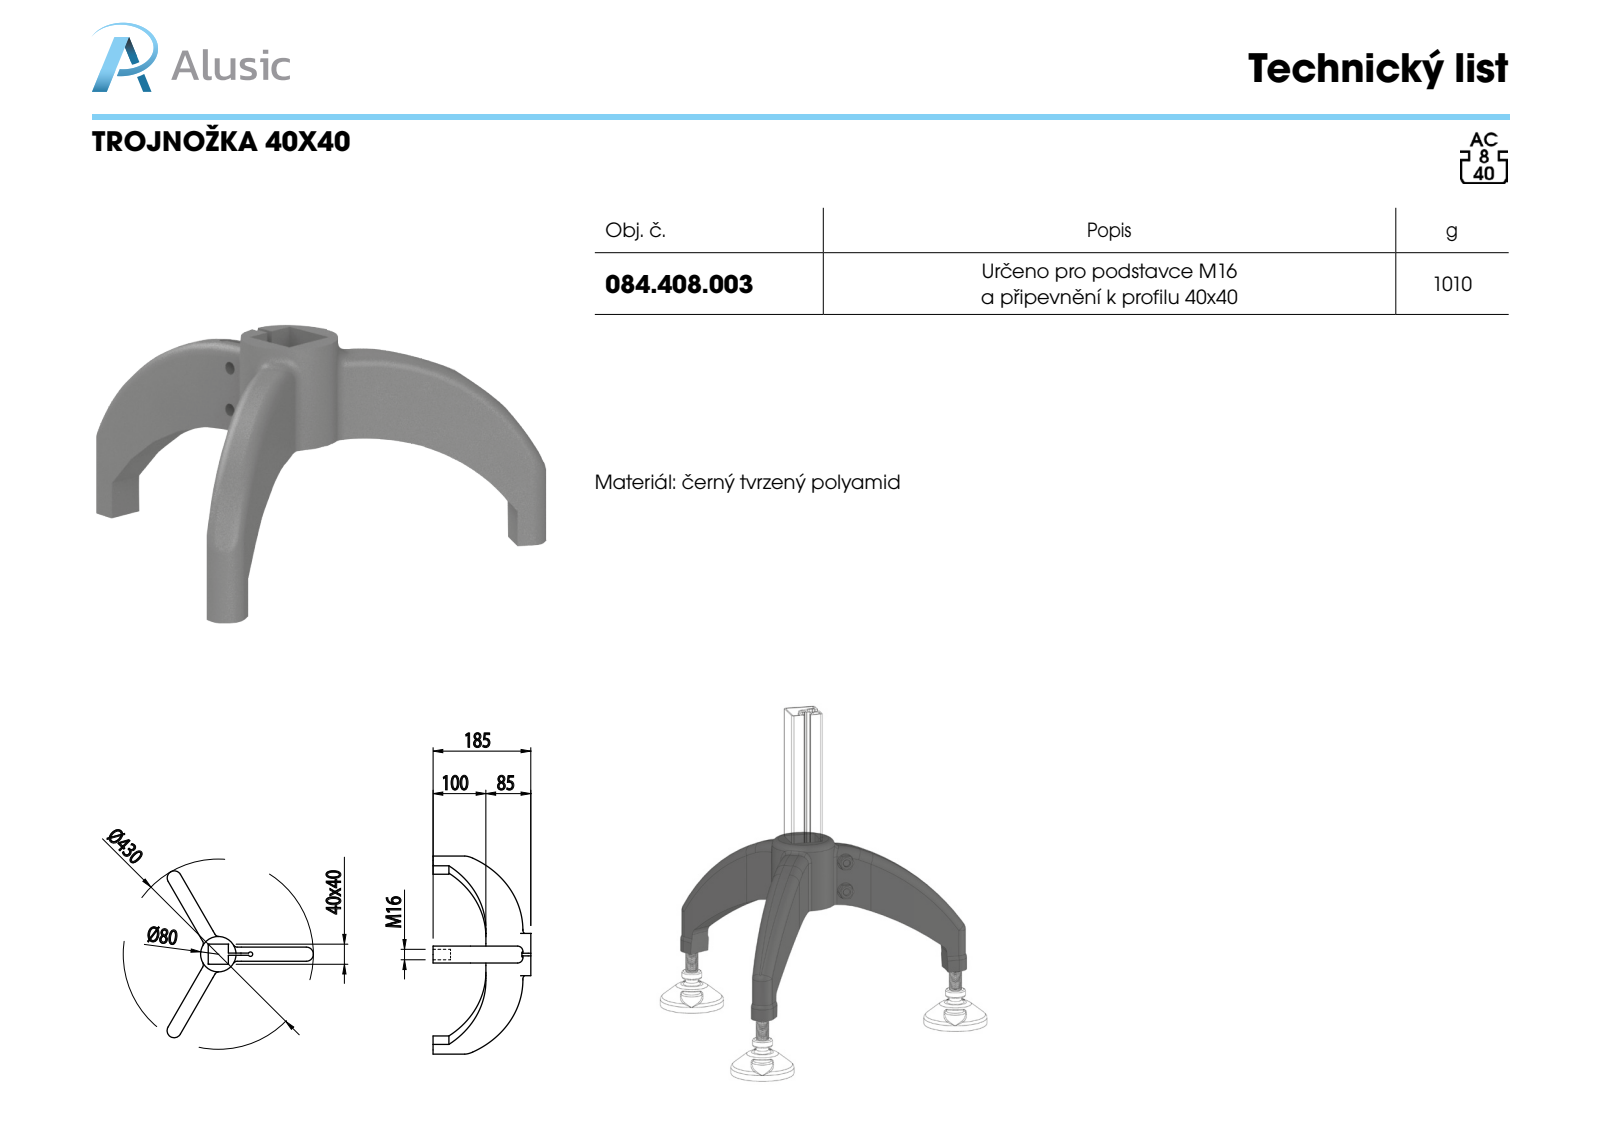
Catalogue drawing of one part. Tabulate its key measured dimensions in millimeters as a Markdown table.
| quantity | value |
| --- | --- |
| part name | 084.408.003 |
| STEP written by | SolidWorks 2016 (CONFIG_CONTROL_DESIGN) |
| units | millimeters |
| bodies | 0 solids, 222 faces (54 planar, 60 cylindrical, 108 other) |
| overall size | 375.39 × 328.98 × 185 |
| round holes (diameter × count) | 14 × 3, 10 × 2, 8 × 1 |
| round bosses / shafts (diameter × count) | 21 × 2, 19 × 2 |
| partial cylindrical surfaces (radius × count) | 6 × 6, 1500 × 6, 1501.5 × 6, 2 × 4, 12.99 × 3, 14.49 × 3, 40 × 1 |
| main face-to-face distances | 35, 18, 22, 37.5, 15.5, 19.5, 2.5, 40, 4, 100 |
| hole center spacings | 346.41, 38, 130.01, 242.69, 242.7, 346.42 |
